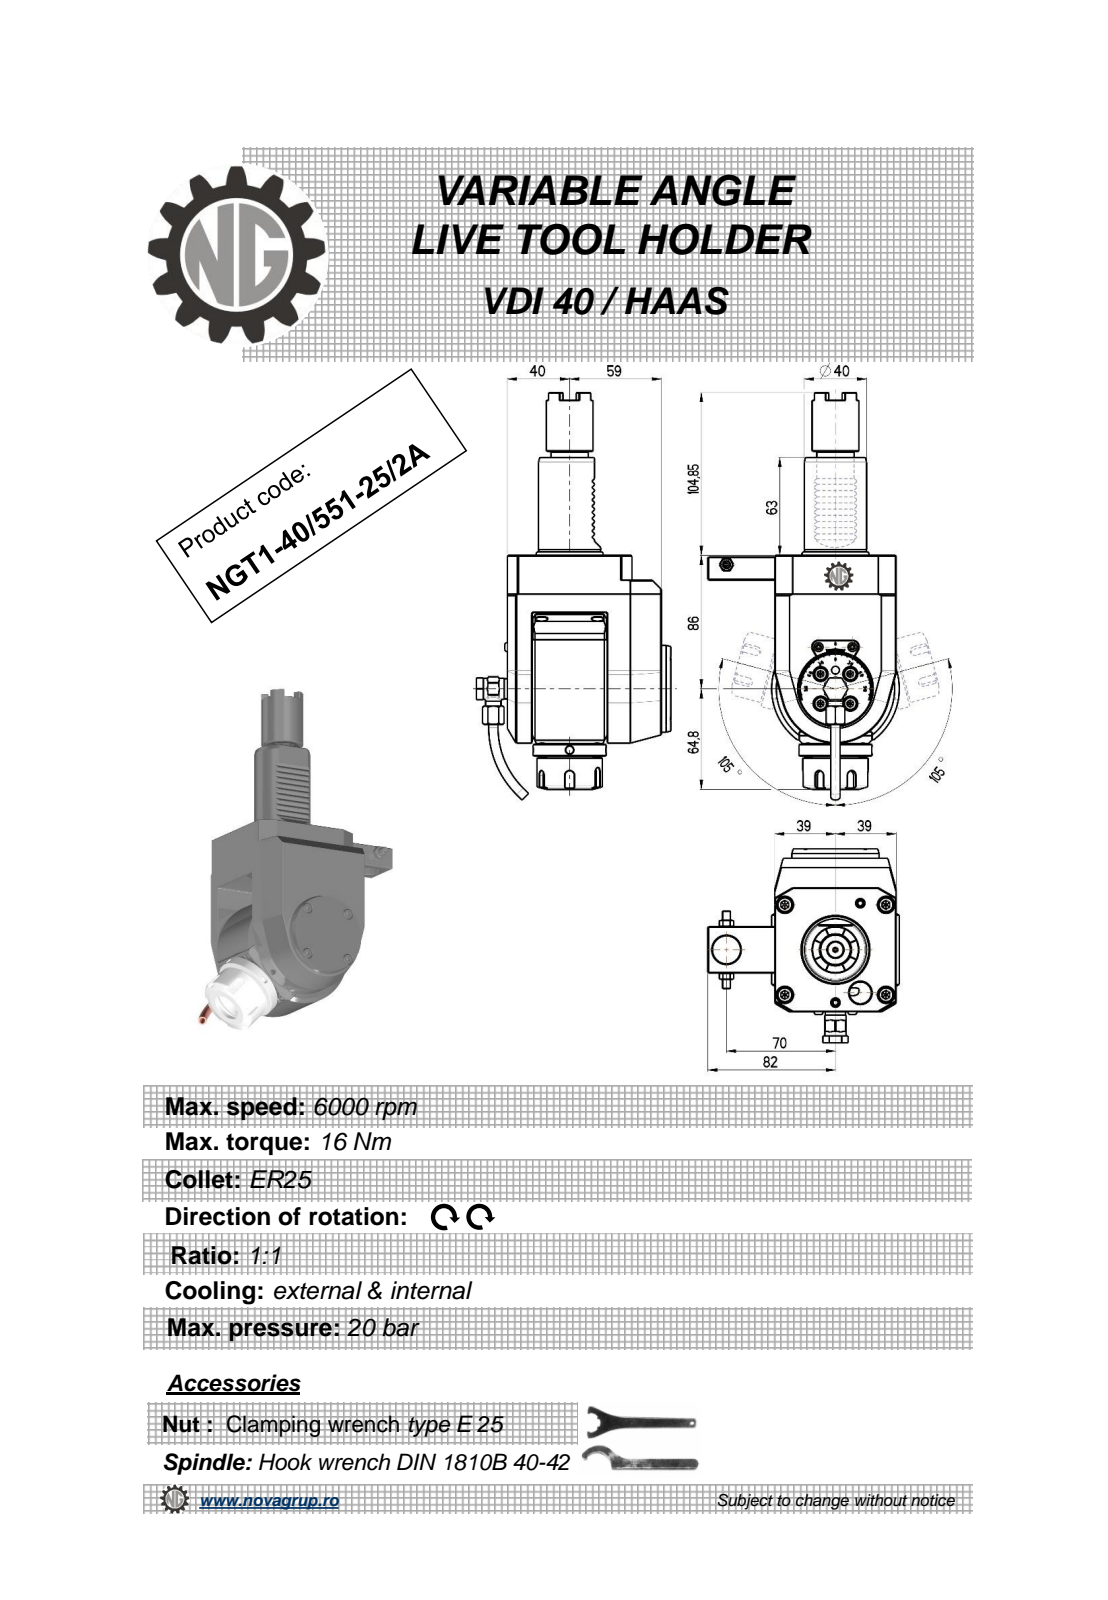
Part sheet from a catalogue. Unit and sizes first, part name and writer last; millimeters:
Units: millimetres
Overall size (bounding box): 262.52 × 124.9 × 123
Round holes (diameter × count): ⌀4 ×3, ⌀5 ×2, ⌀3 ×1, ⌀4.2 ×1, ⌀6.2 ×1, ⌀9 ×1, ⌀9.5 ×1, ⌀11 ×1, ⌀18 ×1, ⌀20.3 ×1
Round bosses / shafts (diameter × count): ⌀10 ×2, ⌀6 ×2, ⌀5.7 ×2, ⌀56 ×1, ⌀47 ×1, ⌀42 ×1, ⌀40 ×1, ⌀36 ×1
Partial cylindrical surfaces — rounded edges, fillets, slot ends (radius × count): R0.26 ×12, R0.3 ×10, R3 ×5, R0.5 ×4, R1 ×2, R10 ×2, R7.7 ×1, R35 ×1
Main face-to-face distances: 16, 37, 64, 99, 78, 6, 105, 1, 21, 25
Hole centre spacings: 0.4, 39.45, 49, 49.4, 70, 85.45, 85.68, 106.3
Volume: 966 311 mm³ · Surface area: 89 555 mm²
Bodies: 1 solid, 621 faces (276 planar, 146 cylindrical, 199 other)
Part name (STEP PRODUCT): NGT1_40_551_25_2A
STEP written by: PRO/ENGINEER BY PARAMETRIC TECHNOLOGY CORPORATION, 2010280 (CONFIG_CONTROL_DESIGN)
